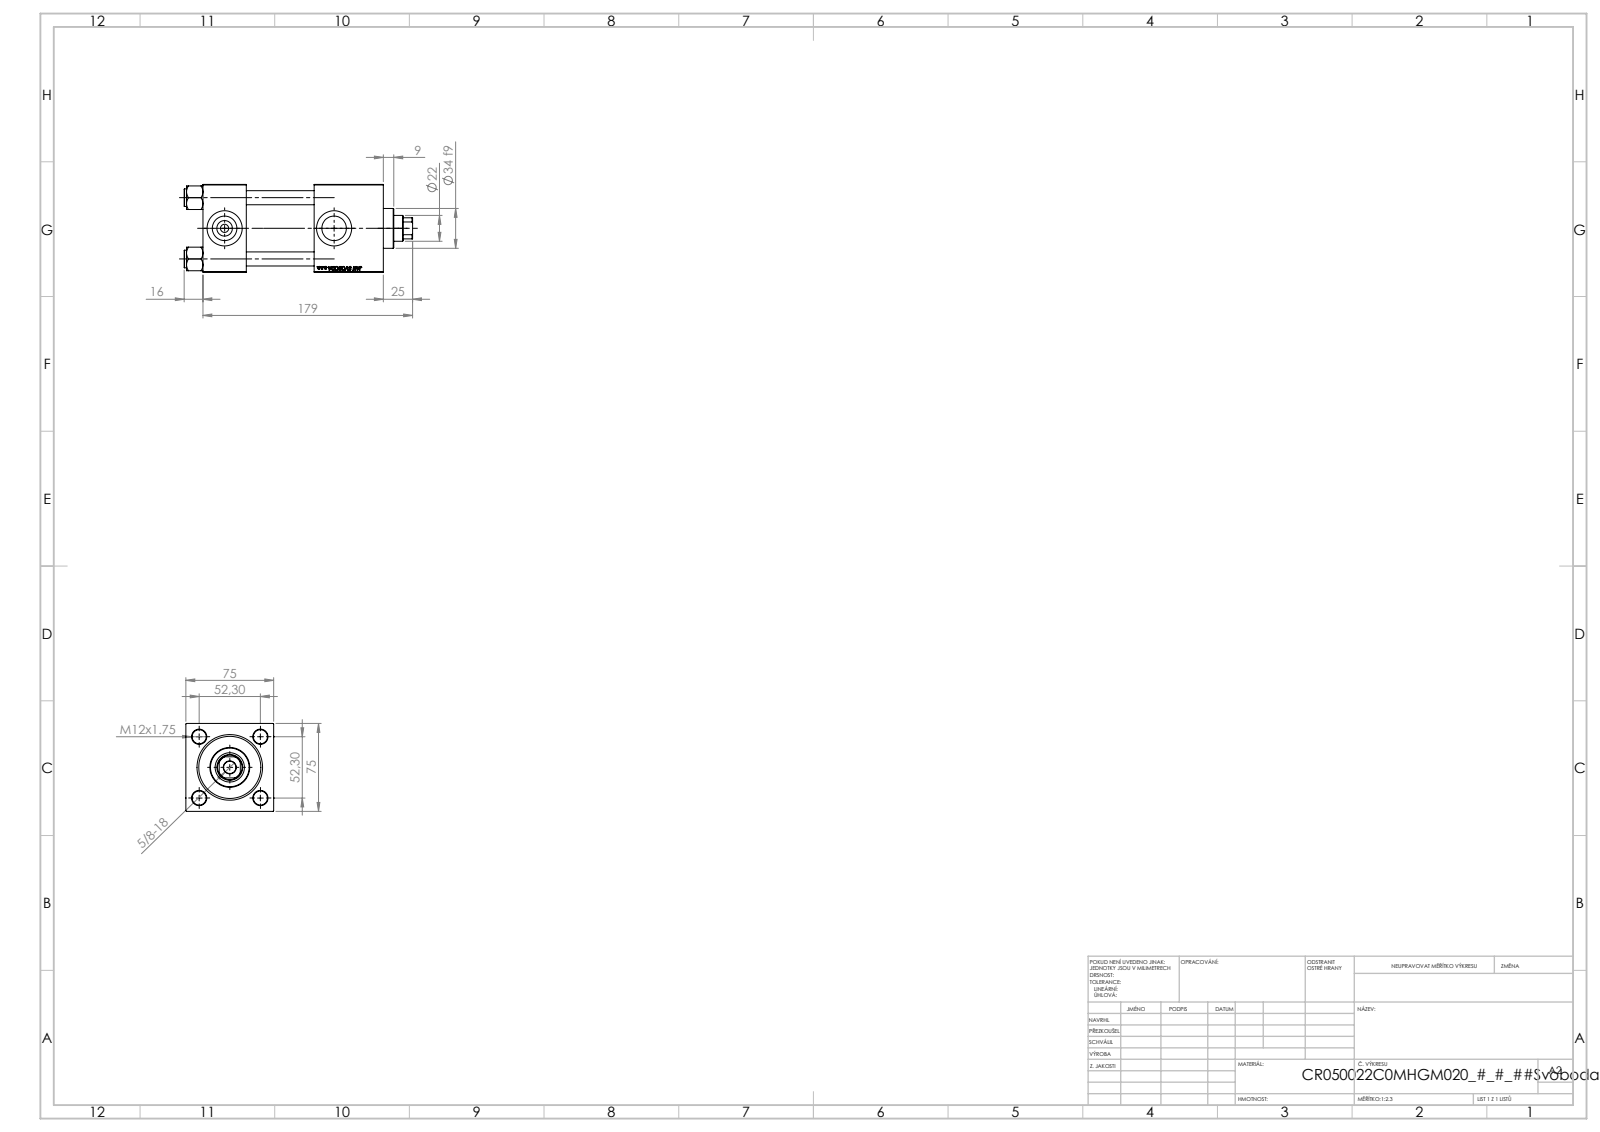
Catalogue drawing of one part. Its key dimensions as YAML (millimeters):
part_name: "NUT_M5_C; V215CR_C_TYCINKA; V215CR_VCP_C; V215CR_C_Body (+1 more)"
step_written_by: "SolidWorks 2019 (CONFIG_CONTROL_DESIGN)"
units: millimeters
bodies: {solids: 11, faces: 1148, planar: 526, cylindrical: 86, other: 536}
overall_size: [195, 75.54, 75]
volume: 656964
surface_area: 147285
round_holes:
  - {diameter: 12, count: 4}
  - {diameter: 7, count: 2}
  - {diameter: 20.96, count: 2}
  - {diameter: 30, count: 2}
  - {diameter: 10.5, count: 1}
  - {diameter: 22, count: 1}
  - {diameter: 25, count: 1}
  - {diameter: 41, count: 1}
  - {diameter: 50, count: 1}
  - {diameter: 53, count: 1}
round_bosses_or_shafts:
  - {diameter: 15, count: 4}
  - {diameter: 56, count: 1}
  - {diameter: 34, count: 1}
partial_cylinders:
  - {radius: 10.5, count: 1}
face_to_face_distances: [75, 37, 154, 117, 95, 58, 59, 125.3, 88.3, 30.3]
hole_center_spacings: [36.98, 52.3, 73.96, 93.5]
